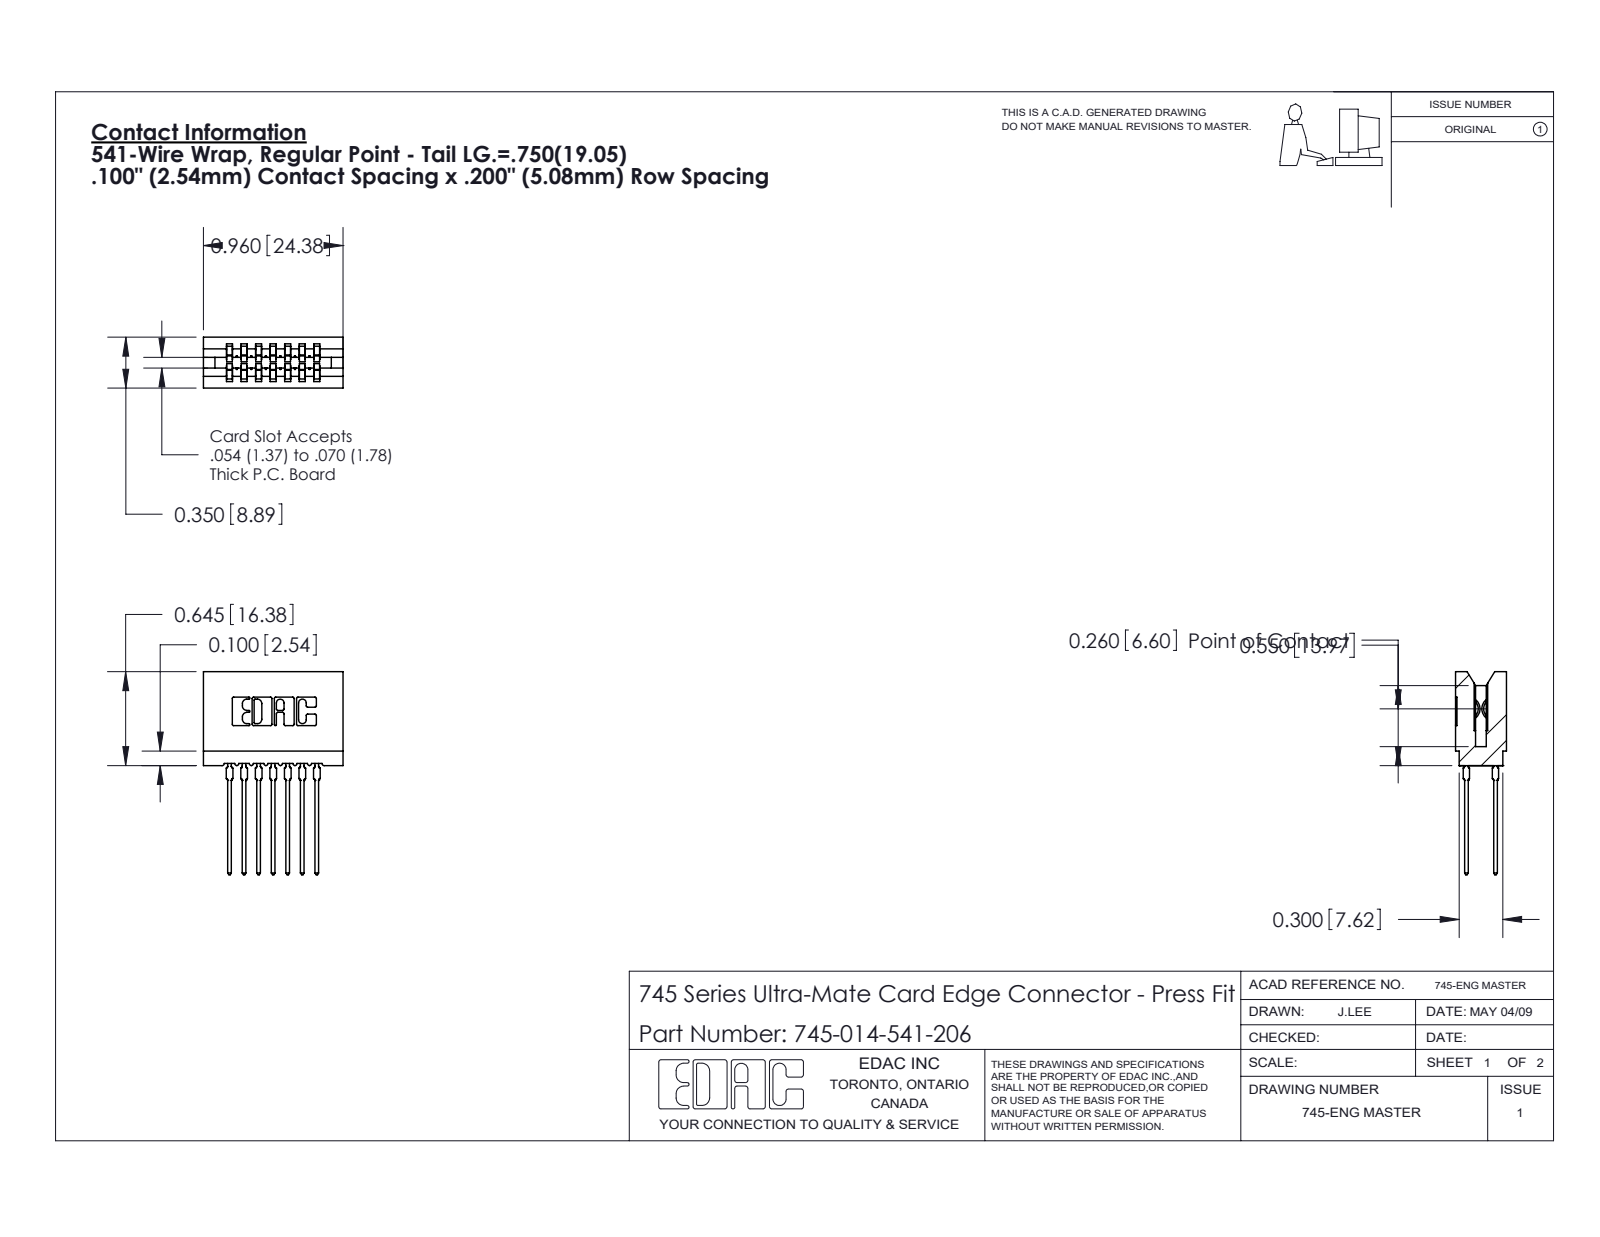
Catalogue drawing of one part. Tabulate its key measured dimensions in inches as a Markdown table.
| quantity | value |
| --- | --- |
| part name | 745-014-541-206; 745 Part_Insulator Option - 06; 745-292-001_541 |
| STEP written by | SolidWorks 2020 (CONFIG_CONTROL_DESIGN) |
| units | inches |
| bodies | 15 solids, 1349 faces (700 planar, 285 cylindrical, 364 other) |
| overall size | 1.396 × 0.96 × 0.35 |
| volume | 0.15 in³ |
| surface area | 6.948 in² |
| partial cylindrical surfaces (radius × count) | 0.021 × 28, 0.01 × 22, 0.015 × 14, 0.005 × 8, 0.011 × 8, 0.007 × 6, 0.031 × 6, 0.026 × 3 |
| main face-to-face distances | 0.2, 0.1, 0.3, 0.042, 0.142, 0.4, 0.058, 0.242, 0.158, 0.063 |
